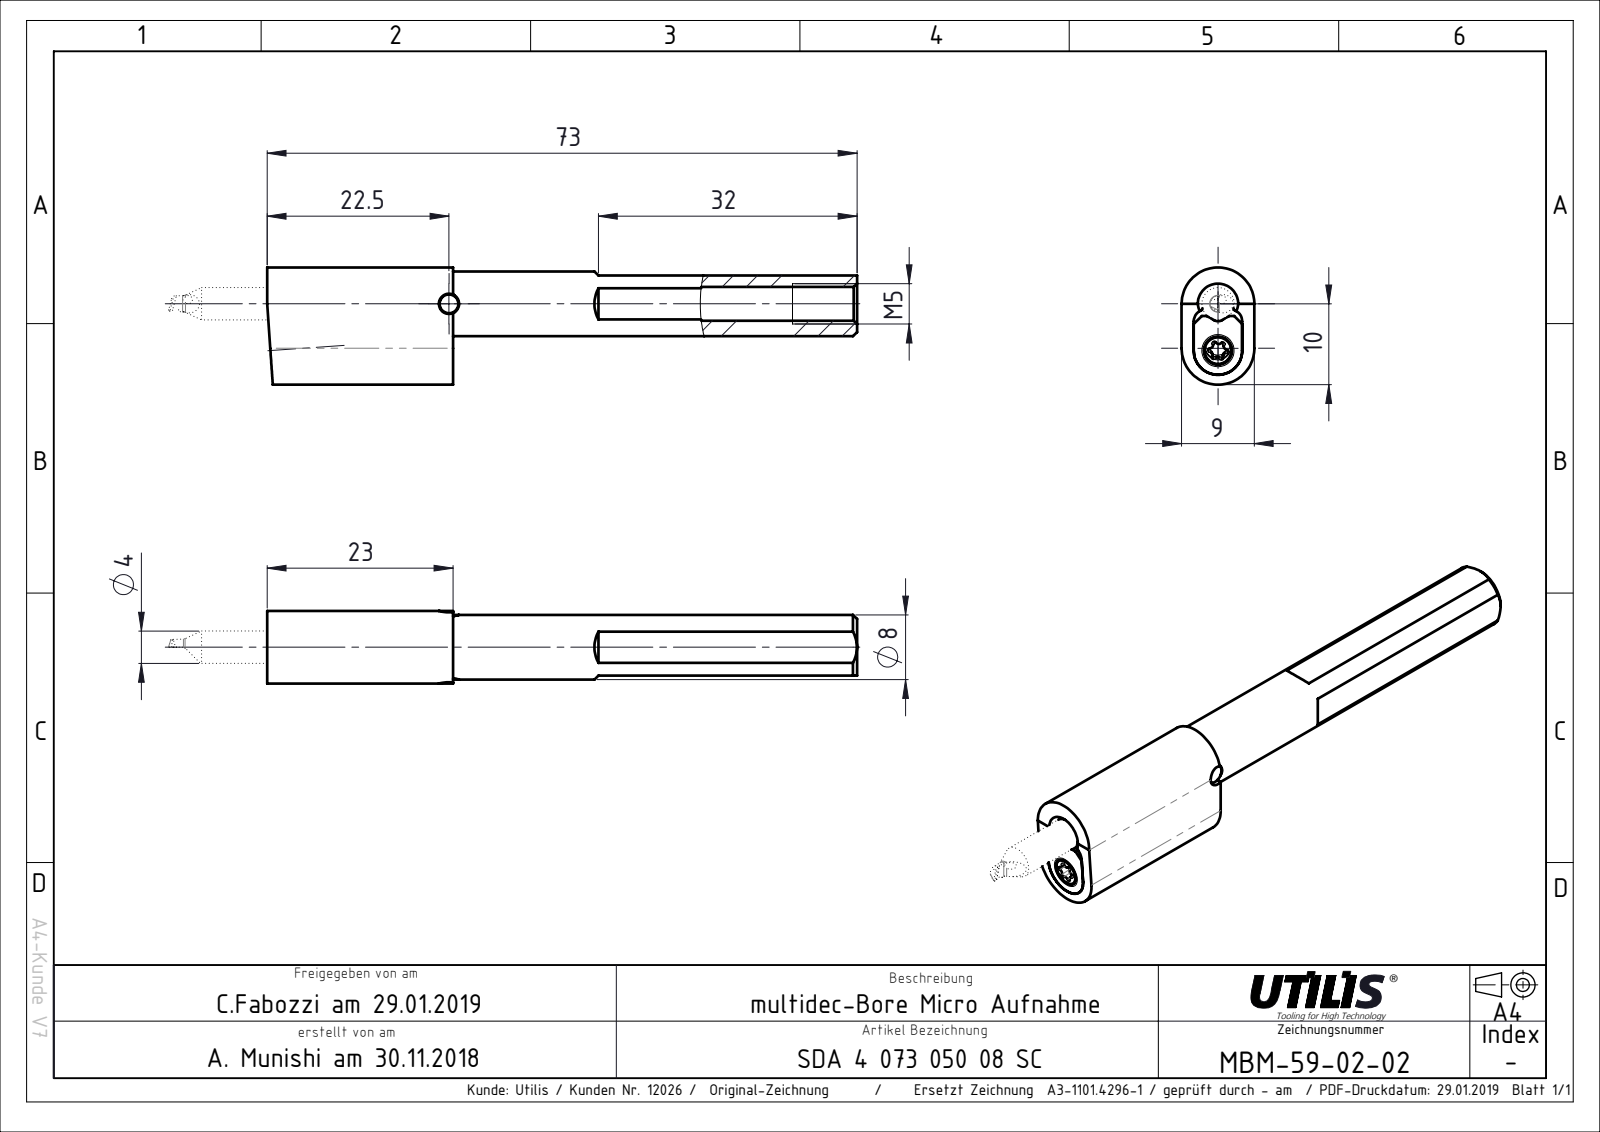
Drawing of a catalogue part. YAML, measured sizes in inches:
part_name: "MBM-59-02-02"
step_written_by: "SolidWorks 2018 (CONFIG_CONTROL_DESIGN)"
units: inches
bodies: {solids: 1, faces: 46, planar: 14, cylindrical: 16, other: 16}
overall_size: [2.874, 0.571, 0.354]
volume: 0.218
surface_area: 5.462
round_holes:
  - {diameter: 0.098, count: 1}
  - {diameter: 0.13, count: 1}
  - {diameter: 0.157, count: 1}
  - {diameter: 0.165, count: 1}
round_bosses_or_shafts:
  - {diameter: 0.315, count: 1}
partial_cylinders:
  - {radius: 0.177, count: 2}
  - {radius: 0.118, count: 1}
face_to_face_distances: [0.354, 0.315, 0.039, 0.059, 0.295, 0.256, 0.236, 0.02, 0.346, 0.906]
